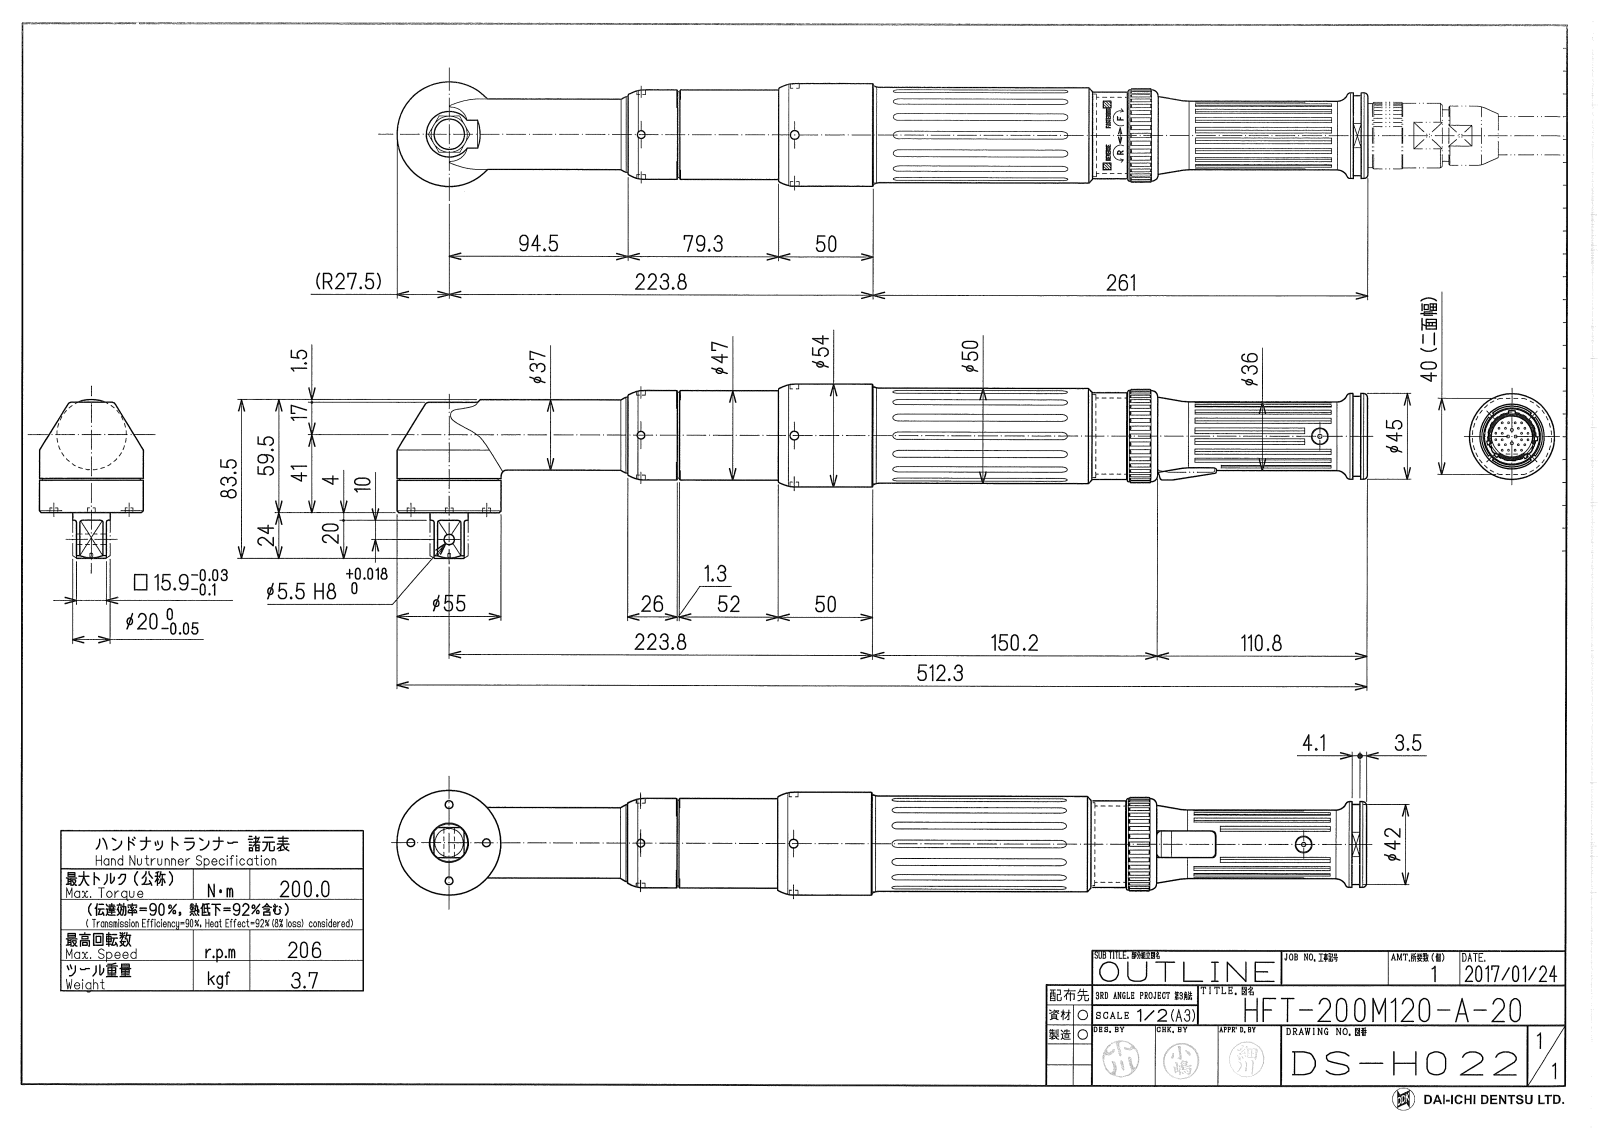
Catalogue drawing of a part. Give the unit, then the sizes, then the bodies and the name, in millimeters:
Units: millimetres
Overall size (bounding box): 512.25 × 92 × 55
Round holes (diameter × count): ⌀4.1 ×4, ⌀4.6 ×4, ⌀9 ×2, ⌀52.4 ×2, ⌀1.6 ×1, ⌀3 ×1, ⌀5.5 ×1, ⌀6 ×1, ⌀16 ×1, ⌀20.5 ×1, ⌀22.6 ×1, ⌀23.8 ×1
Round bosses / shafts (diameter × count): ⌀1 ×24, ⌀1.6 ×4, ⌀52 ×2, ⌀8 ×2, ⌀55 ×1, ⌀54 ×1, ⌀50 ×1, ⌀48 ×1
Partial cylindrical surfaces — rounded edges, fillets, slot ends (radius × count): R0.1 ×36, R1.5 ×36, R0.33 ×18, R3 ×18, R0.3 ×6, R1 ×6, R2.5 ×6, R0.88 ×2
Main face-to-face distances: 34.96, 3.5, 15.88, 41, 1, 1.5, 15.4, 11.9, 3, 40
Hole centre spacings: 20, 28.28, 40, 80.75, 103.45, 183.34, 382.57, 393.56
Volume: 837 405 mm³ · Surface area: 91 900 mm²
Bodies: 1 solid, 834 faces (433 planar, 279 cylindrical, 122 other)
Part name (STEP PRODUCT): HFT-200M120-A-20(DS-H022+A)_OUTLINE
STEP written by: Autodesk Inventor 2017 (AUTOMOTIVE_DESIGN)
